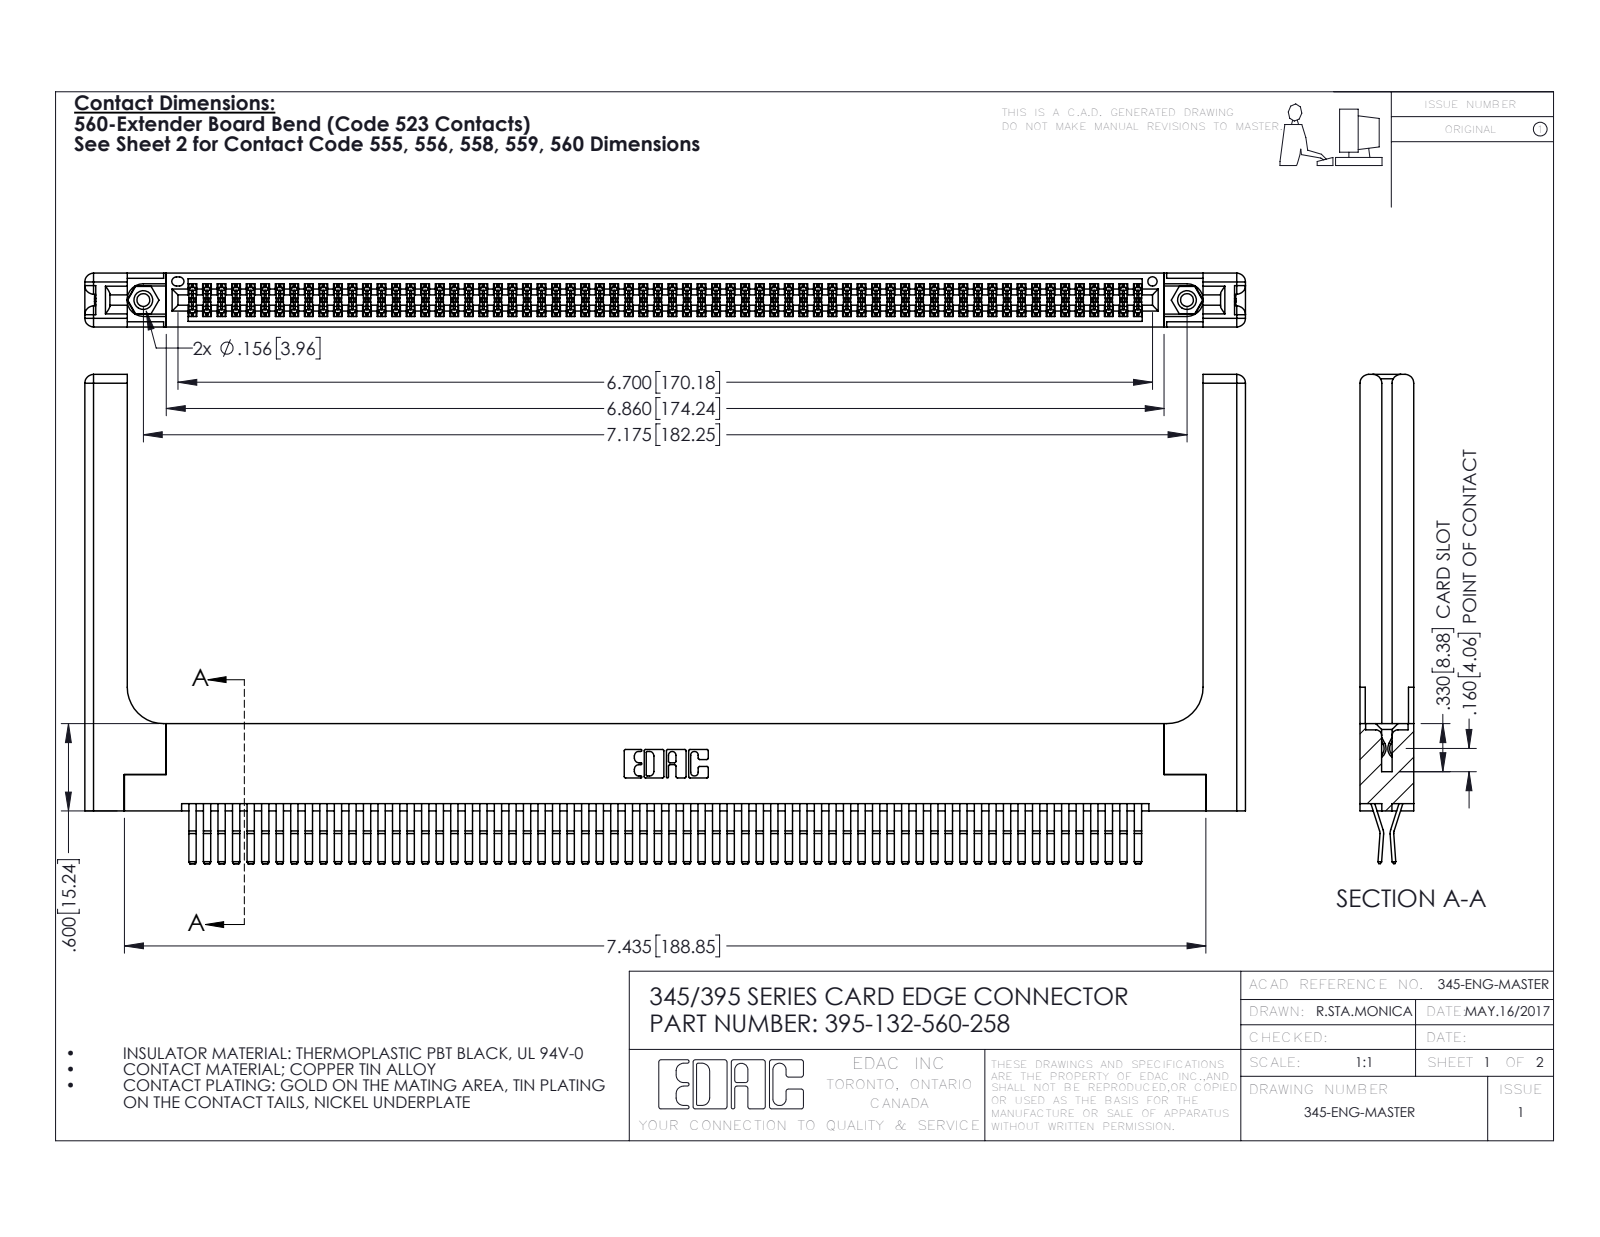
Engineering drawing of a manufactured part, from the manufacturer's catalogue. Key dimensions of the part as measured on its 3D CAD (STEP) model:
Part name (STEP PRODUCT): 345-250-001_345-250-001-102; 345-292-001_560 Tail; 395-132-560-258; 345-220-058_345-220-058 (+1 more)
STEP written by: SolidWorks 2016 (CONFIG_CONTROL_DESIGN)
Units: inches
Bodies: 137 solids, 7246 faces (4584 planar, 2602 cylindrical, 60 other)
Overall size (bounding box): 7.979 × 3.362 × 0.37
Volume: 1.785 in³ · Surface area: 59.61 in²
Round holes (diameter × count): ⌀0.089 ×2, ⌀0.125 ×2, ⌀0.156 ×2, ⌀0.064 ×1
Round bosses / shafts (diameter × count): ⌀0.155 ×2
Partial cylindrical surfaces — rounded edges, fillets, slot ends (radius × count): R0.006 ×199, R0.01 ×22, R0.06 ×16, R0.007 ×6, R0.031 ×6, R0.026 ×3, R0.01 ×2, R0.014 ×2
Main face-to-face distances: 0.072, 0.298, 0.025, 0.37, 0.2, 0.098, 0.272, 0.225, 0.148, 0.15
Hole centre spacings: 0.27, 6.939, 7.175
